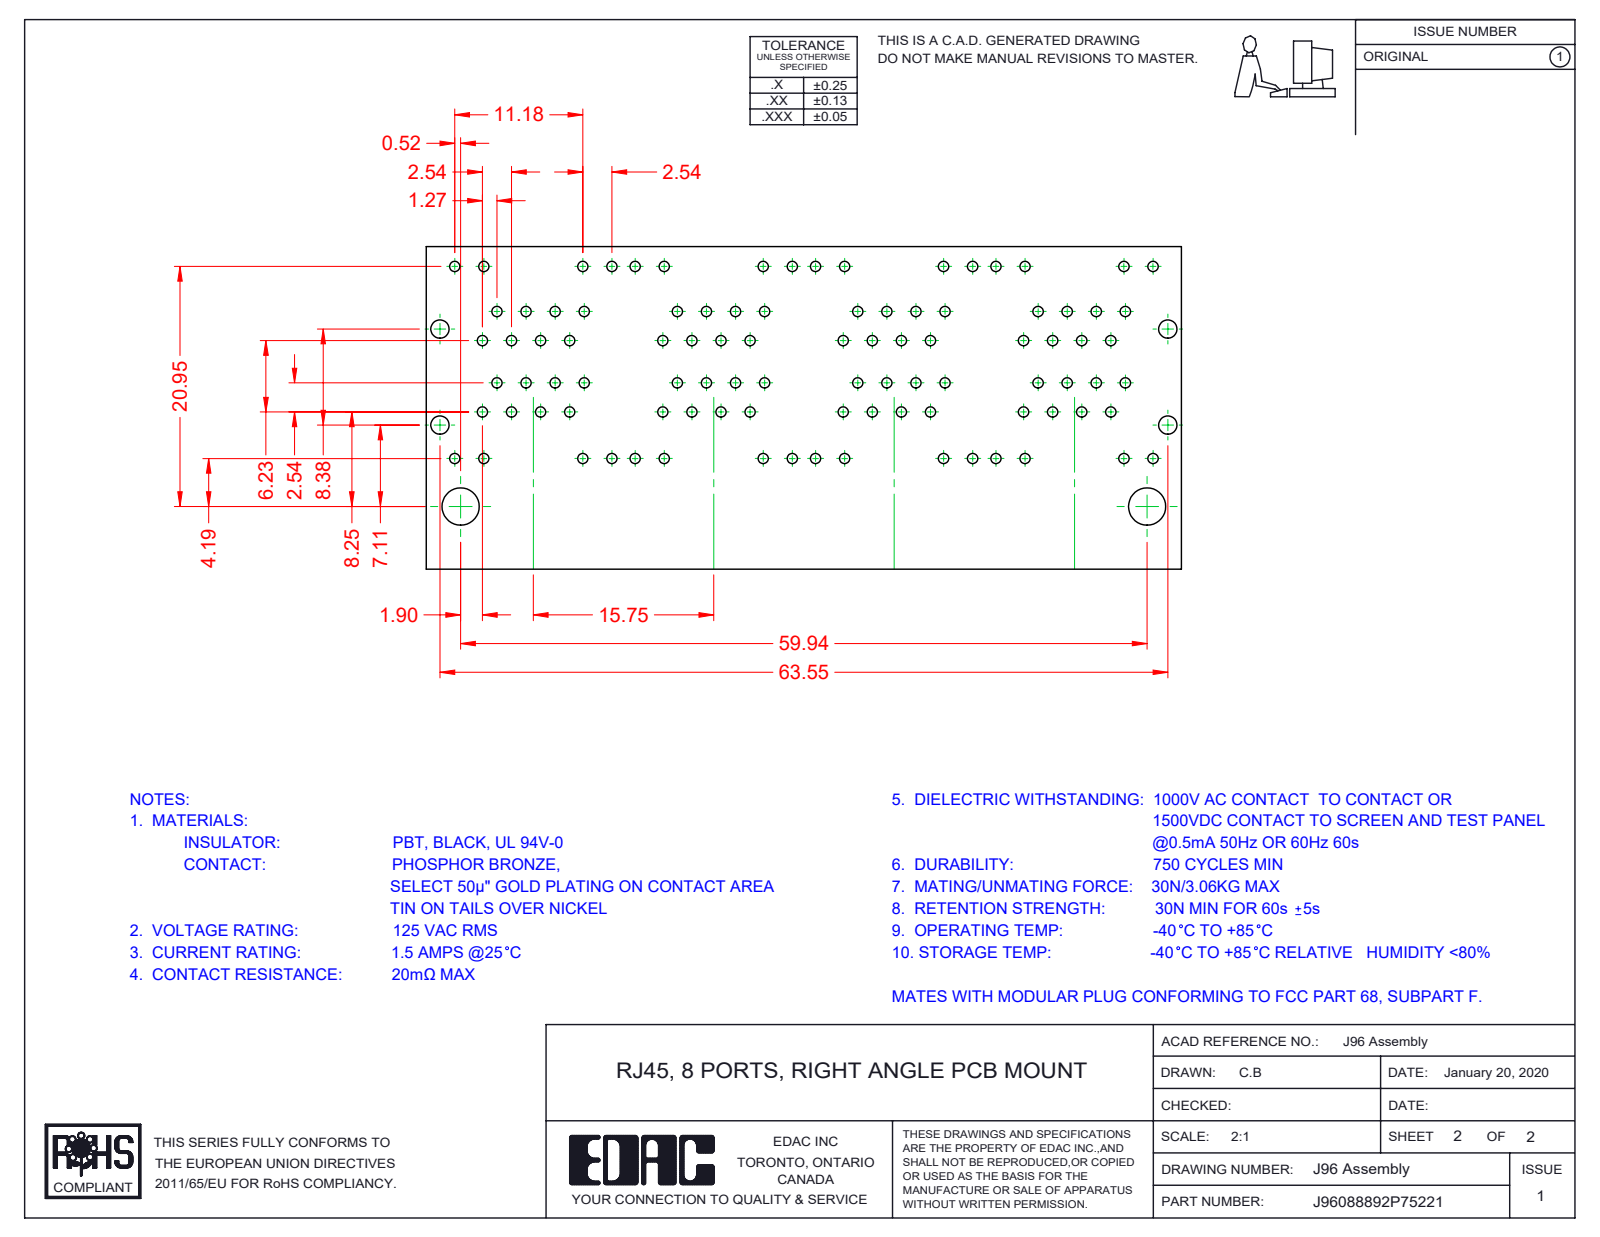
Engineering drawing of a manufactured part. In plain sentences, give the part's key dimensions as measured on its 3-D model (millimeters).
The part is named "96 Contact Lock Lower; 96 Contacts Upper; 96 Insulator Insert; 96 Insulator_8 Ports (+8 more)". Its 3-D file was written by "SolidWorks 2016 (CONFIG_CONTROL_DESIGN)". It is 96 solids with 7836 faces: 6105 planar, 1420 cylindrical and 311 other. Overall it measures 67.35 by 31.38 by 28.68 millimeters. Its volume is 24 149 cubic millimeters and its surface area 63 596 square millimeters. Round holes: 3 of diameter 1.7. Round bosses or shafts: 3 of diameter 1.68. Partial cylindrical surfaces (rounded edges, fillets, slot ends): 124 of radius 0.25, 73 of radius 0.35, 72 of radius 1, 49 of radius 0.5, 32 of radius 0.91, 27 of radius 0.2, 14 of radius 0.27, 11 of radius 0.7. The main face-to-face distances are 15.75, 0.35, 9.95, 1.17, 1.6, 0.54, 9.98, 10.18, 12.67, 3.37. The hole center spacings are 15.75, 31.5.
